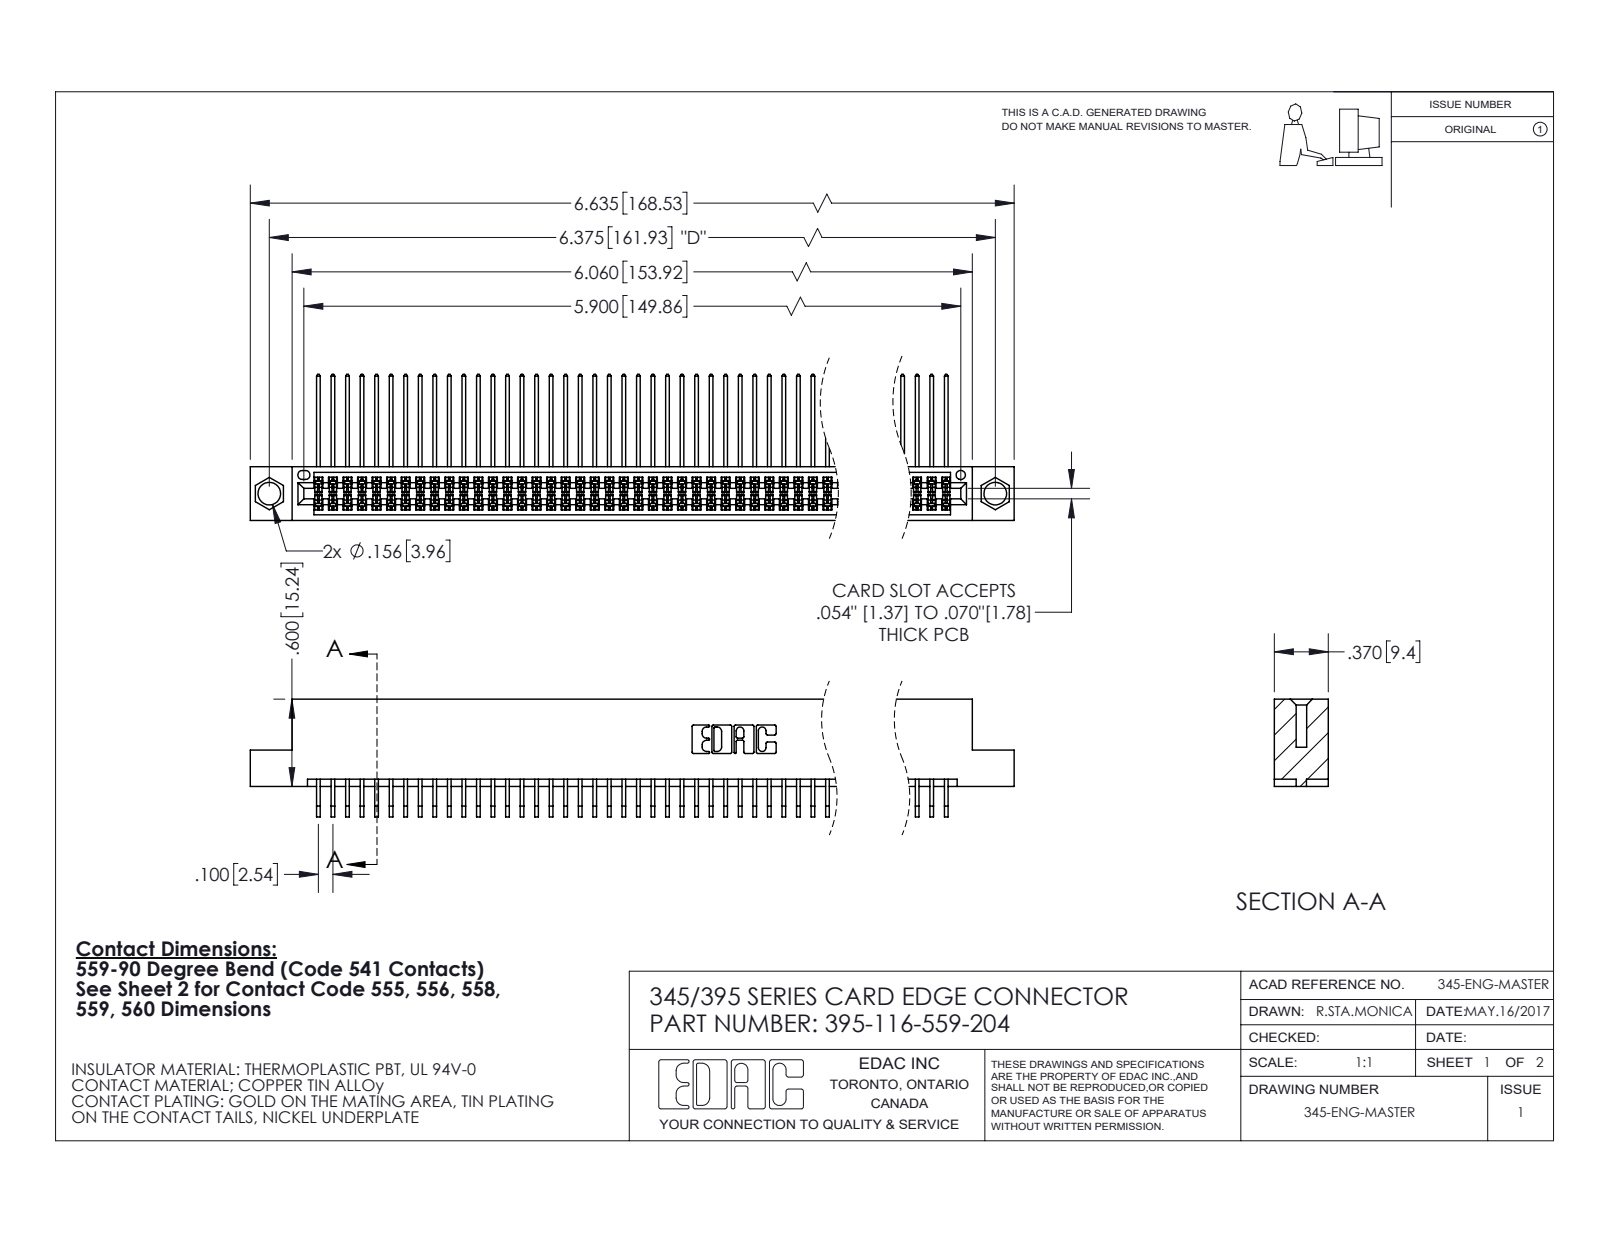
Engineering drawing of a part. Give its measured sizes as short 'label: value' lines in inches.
name: 345-292-001_559 Tail - 2; 345 Part_Flush Mounting Lugs - 0.156 Dia-TI; 345-292-001_558 559 Tail - 1; 395-116-559-204
written by: SolidWorks 2020 (CONFIG_CONTROL_DESIGN)
unit: in
bodies: 117 solids, 6172 faces (4154 planar, 2018 cylindrical, 0 other)
size: 6.635 × 1.005 × 0.809
volume: 1.042 in³; area: 44.27 in²
holes: 2× ⌀0.156, 1× ⌀0.064
rounds: 174× R0.006, 22× R0.01, 6× R0.007, 6× R0.031, 3× R0.026, 2× R0.014, 2× R0.019, 2× R0.022
face distances: 0.072, 0.298, 0.2, 0.37, 0.098, 0.272, 0.025, 0.225, 0.175, 0.15
hole spacings: 0.27, 6.139, 6.375
